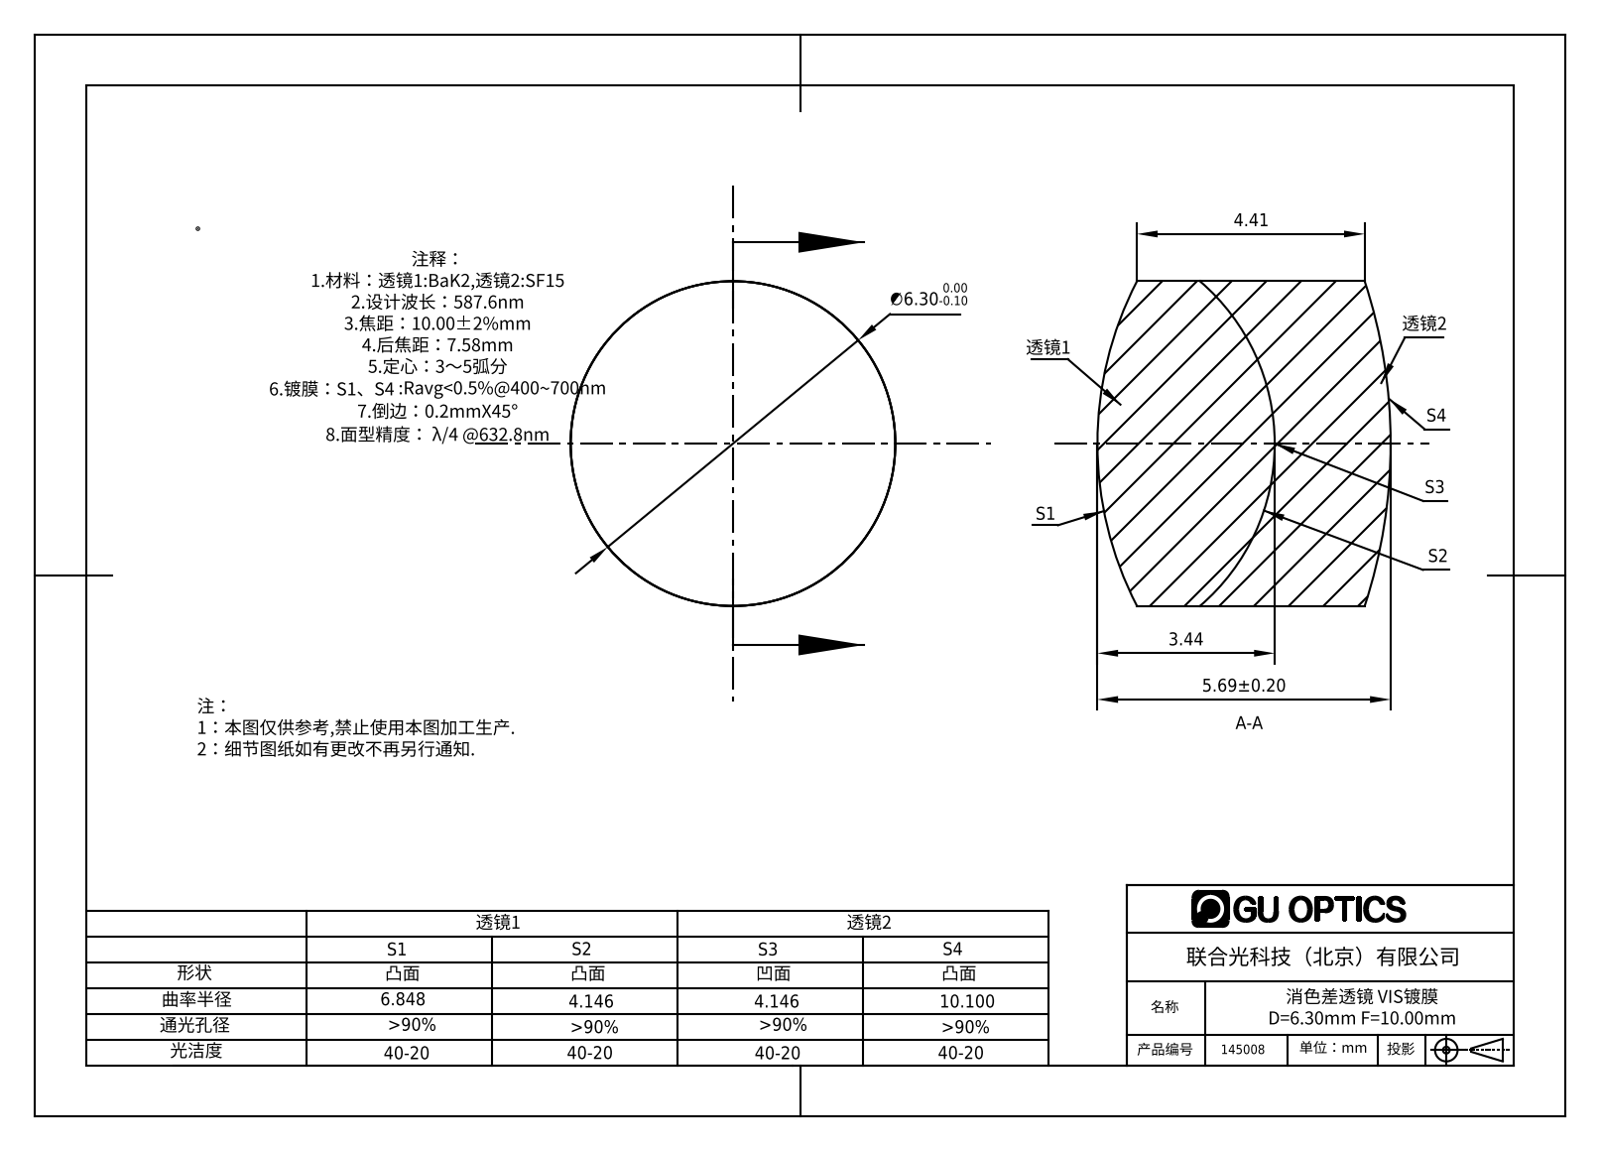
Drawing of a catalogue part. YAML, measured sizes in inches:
part_name: "145008"
step_written_by: "SolidWorks 2016 (AUTOMOTIVE_DESIGN)"
units: inches
bodies: {solids: 2, faces: 12, planar: 0, cylindrical: 4, other: 8}
overall_size: [0.248, 0.248, 0.224]
volume: 0.01
surface_area: 0.353
round_bosses_or_shafts:
  - {diameter: 0.248, count: 1}
